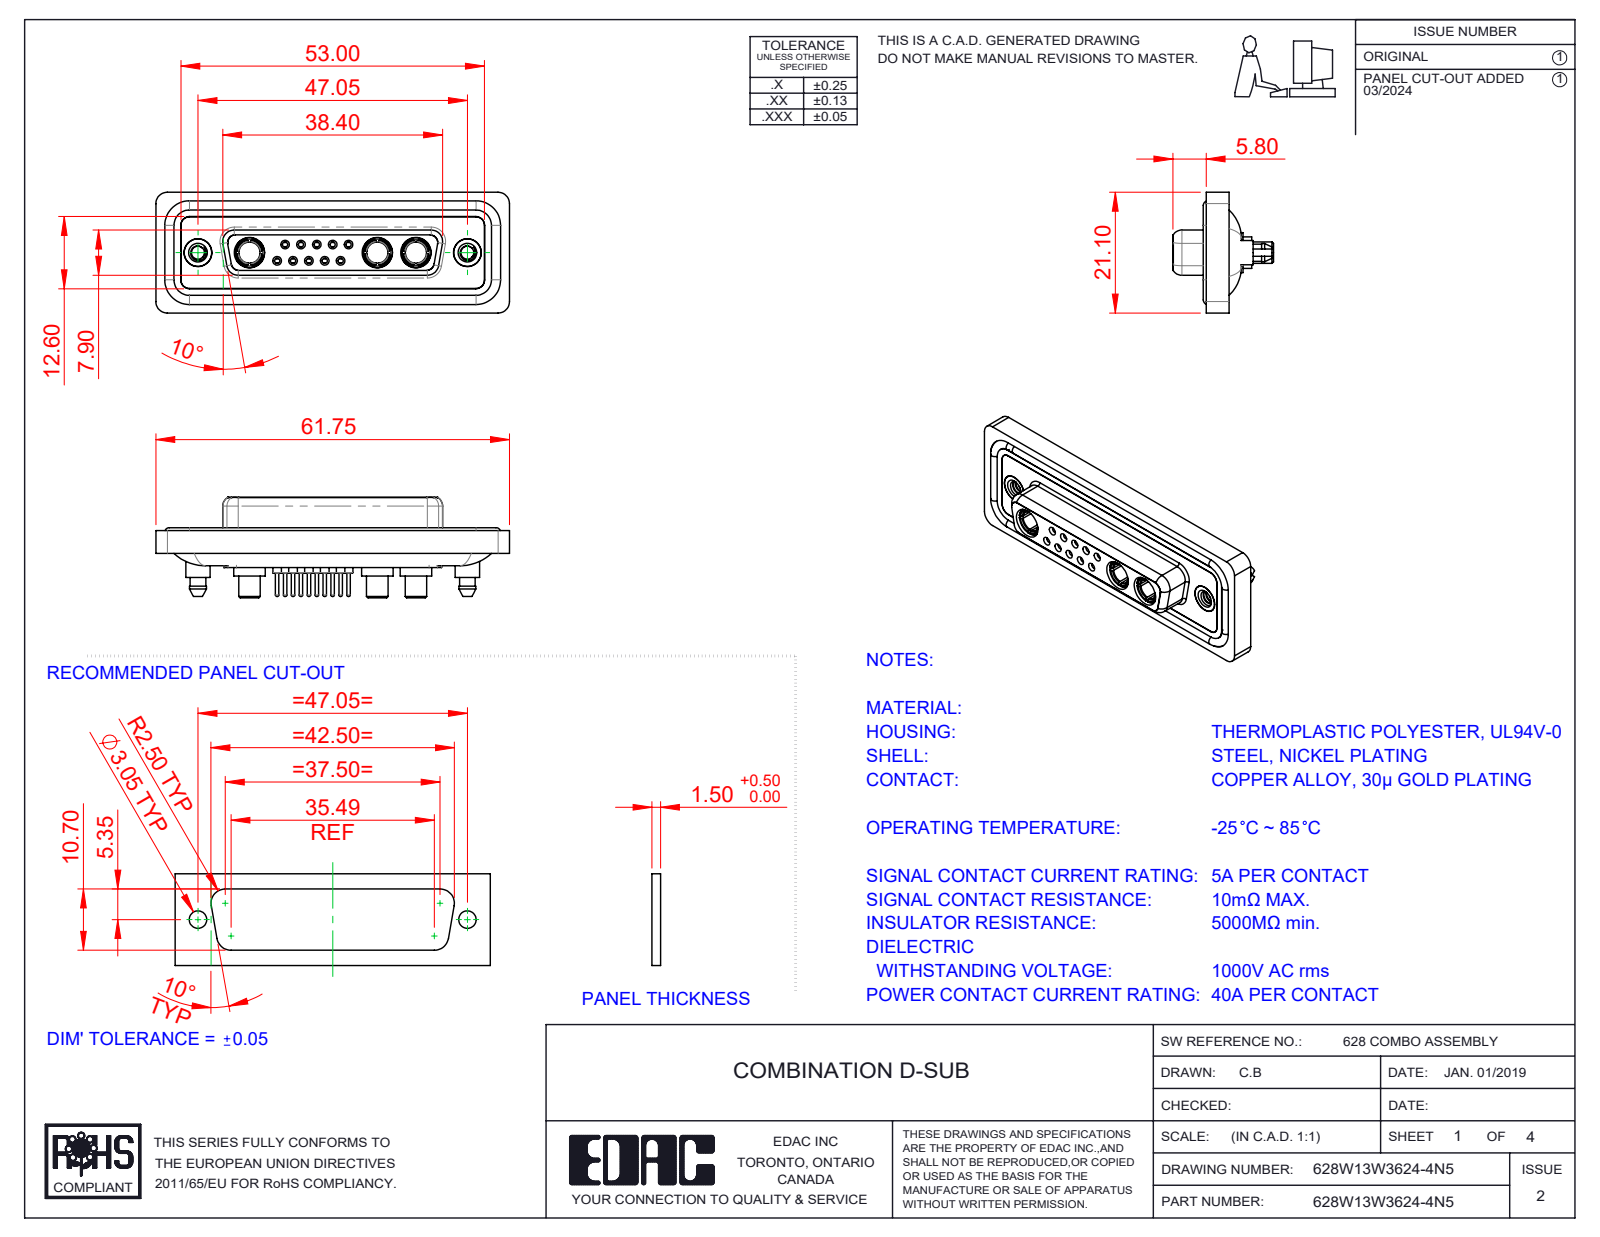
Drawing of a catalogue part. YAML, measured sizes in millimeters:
part_name: "Power Socket_40A S; 628Combo Shell Rear_25 Contacts; 628Combo Shell Front_25 Contacts; 628Combo Contact Row 2_24 (+5 more)"
step_written_by: "SolidWorks 2023 (CONFIG_CONTROL_DESIGN)"
units: millimeters
bodies: {solids: 23, faces: 1208, planar: 358, cylindrical: 479, other: 371}
overall_size: [61.75, 21.1, 17.55]
volume: 8462
surface_area: 14074
round_holes:
  - {diameter: 0.9, count: 10}
  - {diameter: 1.1, count: 10}
  - {diameter: 1.5, count: 10}
  - {diameter: 2, count: 10}
  - {diameter: 1.6, count: 5}
  - {diameter: 1.7, count: 5}
  - {diameter: 4.85, count: 5}
  - {diameter: 3.7, count: 3}
  - {diameter: 5.3, count: 3}
  - {diameter: 2.26, count: 2}
  - {diameter: 4, count: 2}
  - {diameter: 4.05, count: 2}
round_bosses_or_shafts:
  - {diameter: 2.2, count: 10}
  - {diameter: 0.6, count: 10}
  - {diameter: 1.6, count: 9}
  - {diameter: 5.5, count: 3}
  - {diameter: 5.2, count: 3}
  - {diameter: 4.96, count: 3}
  - {diameter: 4.75, count: 3}
  - {diameter: 3.75, count: 3}
partial_cylinders:
  - {radius: 1.5, count: 24}
  - {radius: 2, count: 18}
  - {radius: 1.6, count: 10}
  - {radius: 1.35, count: 8}
  - {radius: 0.25, count: 4}
  - {radius: 0.5, count: 4}
  - {radius: 0.6, count: 4}
  - {radius: 0.65, count: 4}
face_to_face_distances: [0.4, 1.8, 7.45, 5.65, 0.5, 6.6, 7.05, 1.6, 2.9, 1.1]
hole_center_spacings: [3.16, 2.77, 5.03, 5.04, 5.54, 8.31, 7.49, 2.76]
